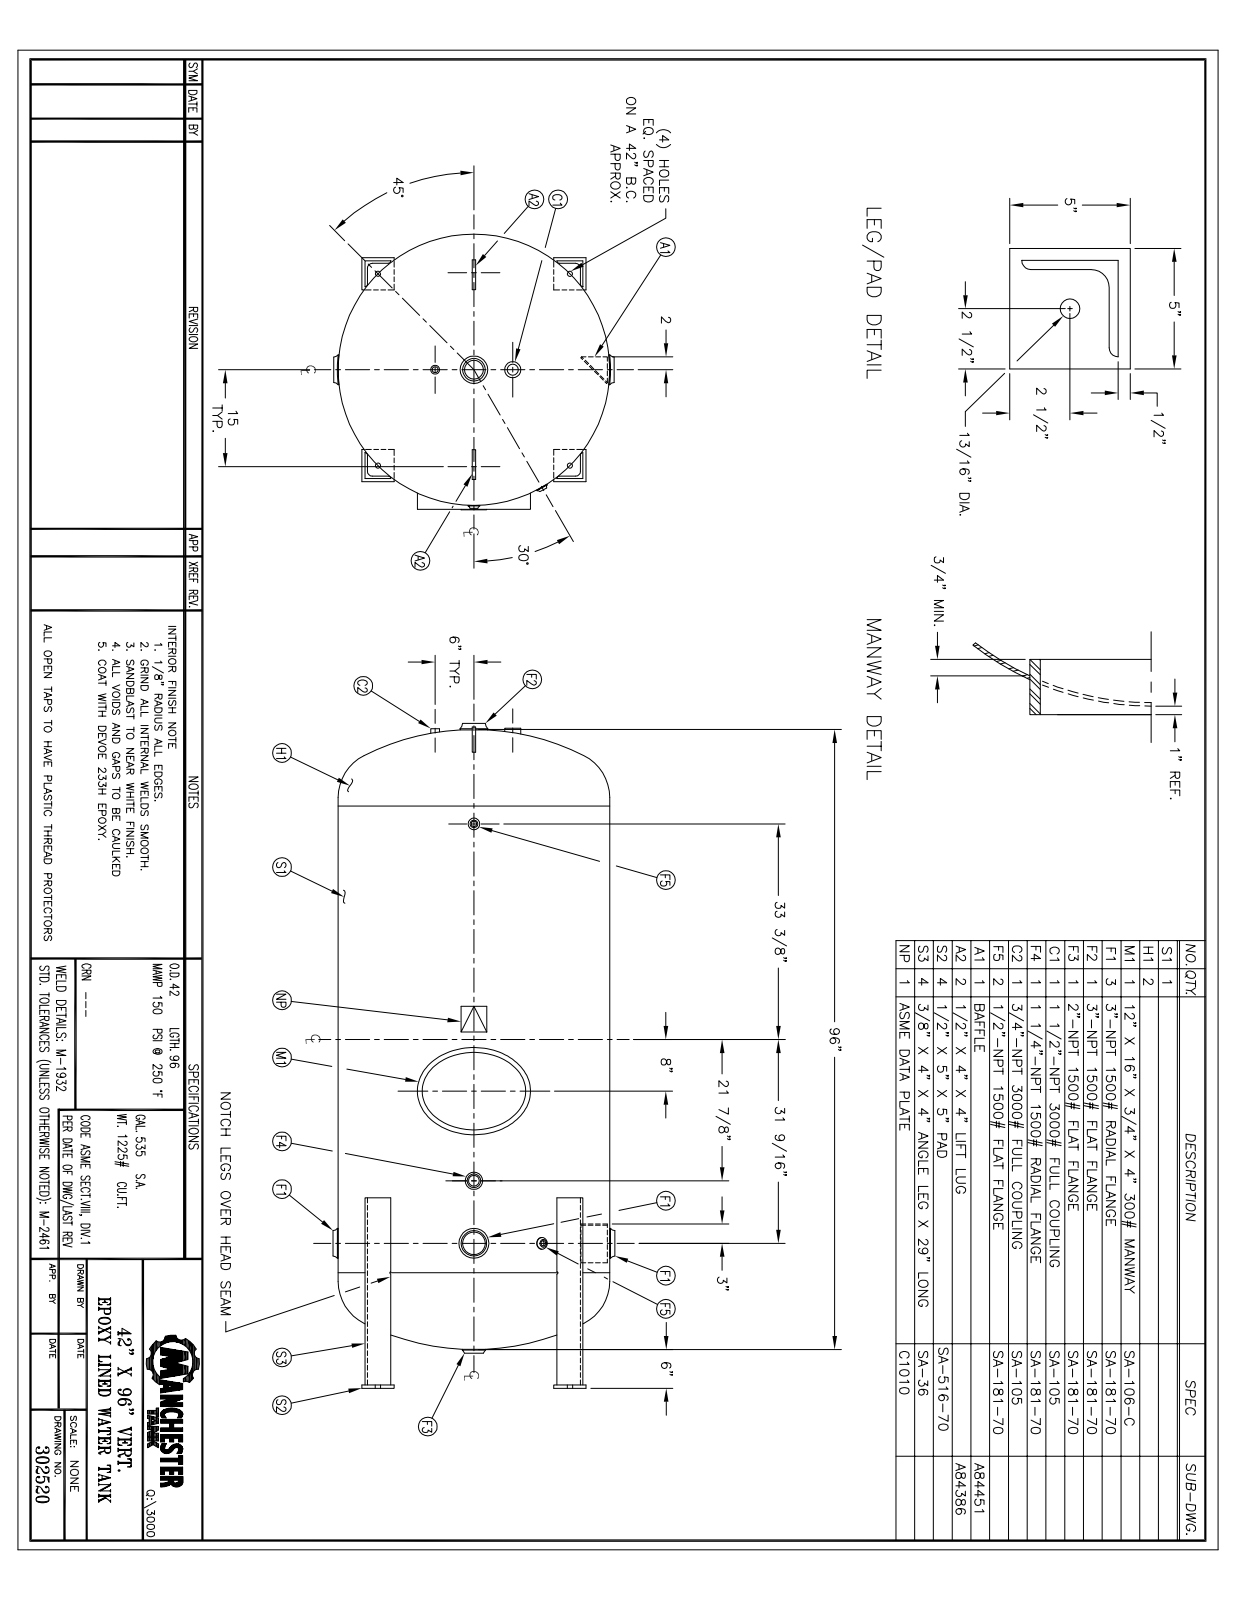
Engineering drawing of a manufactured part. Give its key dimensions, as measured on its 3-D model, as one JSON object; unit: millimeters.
{"part_name": "302520", "step_written_by": "SolidWorks 2011 (CONFIG_CONTROL_DESIGN)", "units": "millimeters", "bodies": {"solids": 0, "faces": 380, "planar": 168, "cylindrical": 120, "other": 92}, "overall_size": [2617.9, 1228.6, 1117.9], "round_holes": [[20.7, 4], [88.9, 3], [21.3, 2], [34.9, 2], [26.7, 1], [38.1, 1], [42.2, 1], [48.3, 1], [60.3, 1], [1044, 1]], "round_bosses_or_shafts": [[123.8, 2], [46.1, 2], [25.4, 2], [1066.8, 1], [1054.1, 1], [117.5, 1], [100, 1], [73, 1]], "partial_cylinders_radius": [[6.4, 9], [9.5, 8], [19.1, 4], [33.5, 4], [50.8, 2], [150.3, 1], [152.4, 1], [534.9, 1]], "face_to_face_distances": [850.3, 9.5, 859.8, 840.8, 12.7, 101.6, 758.2, 748.7, 92.1, 887.1], "hole_center_spacings": [441.7, 536.1, 652.9, 758.2, 152.4, 1072.3, 2033.2, 246]}
